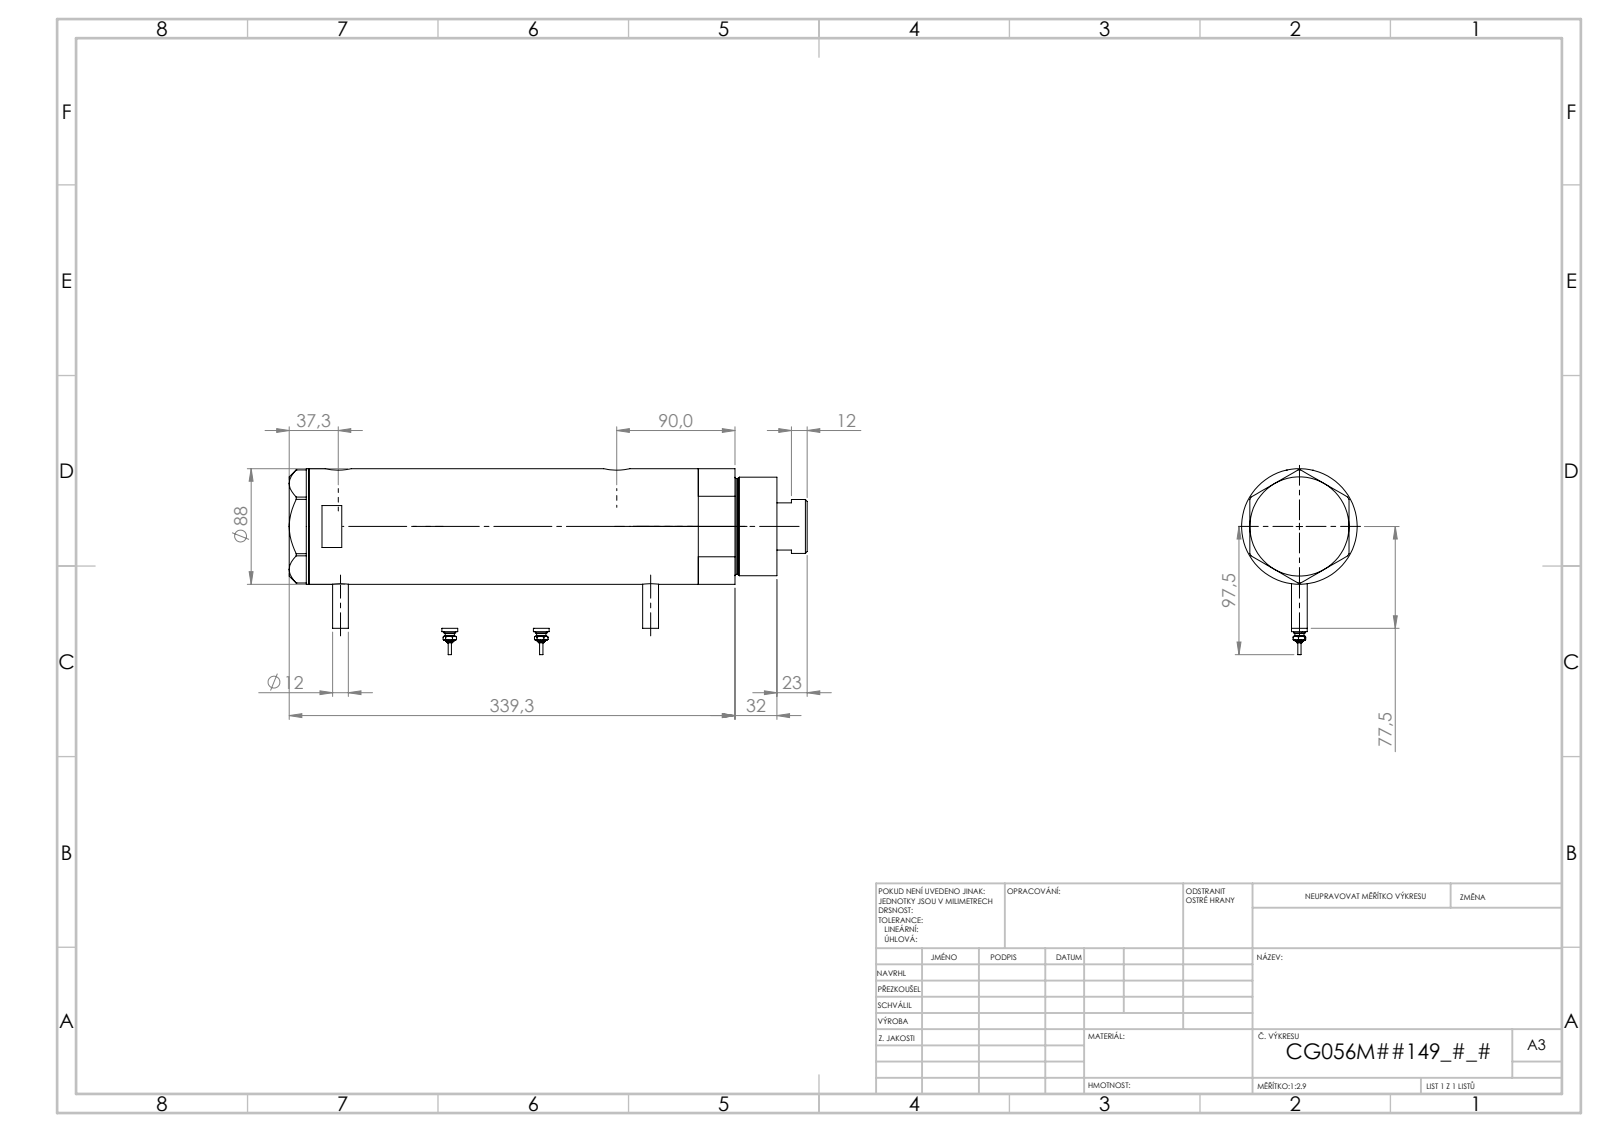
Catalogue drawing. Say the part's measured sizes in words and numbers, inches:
The part is named "Switch; V270CG_MIDDLE; V270CG_FRONT; V270CG_VC (+1 more)". Its 3-D file was written by "SolidWorks 2019 (CONFIG_CONTROL_DESIGN)". It is 6 solids with 213 faces: 80 planar, 69 cylindrical and 64 other. Overall it measures 15.524 by 5.571 by 3.465 inches. Its volume is 124.7 cubic inches and its surface area 438.8 square inches. Round holes: 2 of diameter 0.492, 2 of diameter 0.518, 2 of diameter 0.787, 1 of diameter 0.571, 1 of diameter 1.654, 1 of diameter 1.713, 1 of diameter 2.205, 1 of diameter 2.362, 1 of diameter 3.15. Round bosses or shafts: 4 of diameter 0.472, 2 of diameter 0.354, 2 of diameter 0.276, 2 of diameter 0.177, 2 of diameter 0.098, 1 of diameter 3.465, 1 of diameter 2.953, 1 of diameter 2.874. The main face-to-face distances are 9.228, 1.024, 8.205, 0.591, 1.614, 9.819, 14.028, 14.618, 13.004, 4.799. The hole center spacings are 0.067, 1.016, 8.28, 8.346, 9.295, 9.362.
